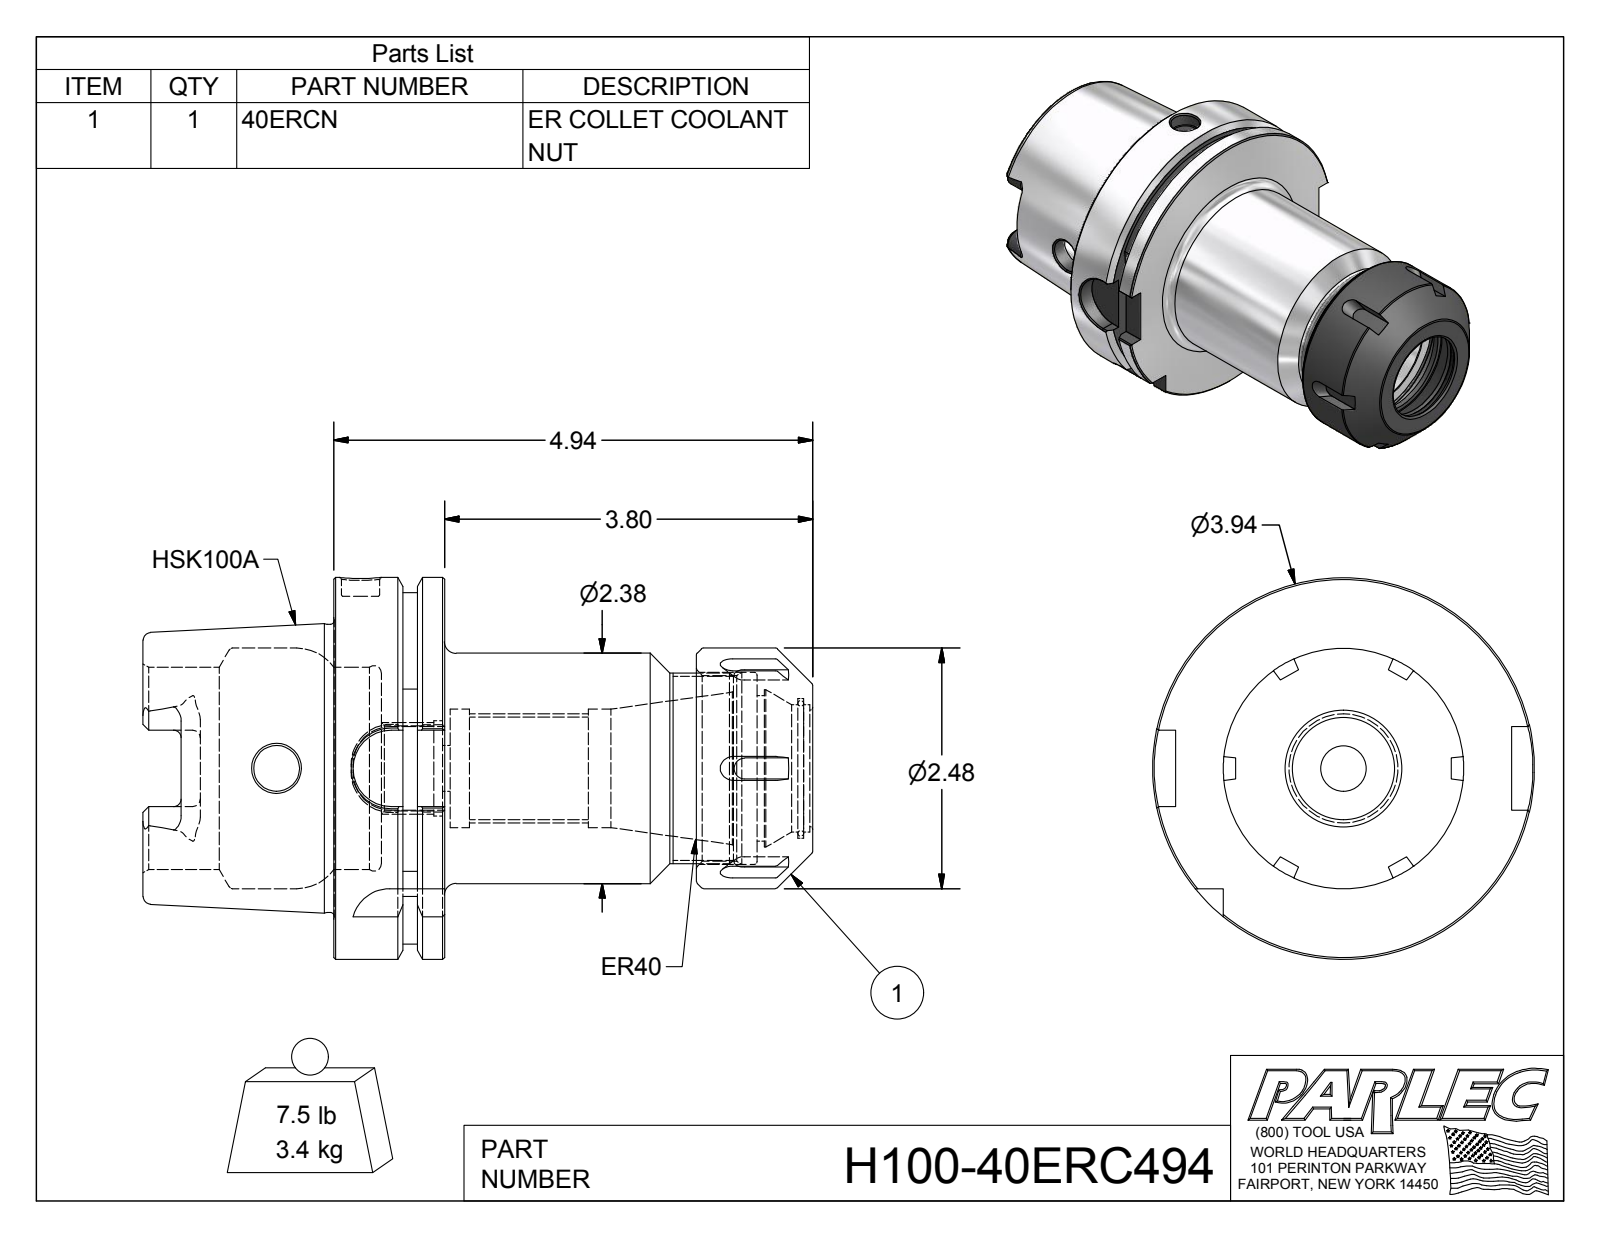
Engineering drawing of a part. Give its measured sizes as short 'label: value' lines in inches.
name: H100-40ERC494; H100-40ER5-1; 40ERCN
written by: Autodesk Inventor 2012 (AUTOMOTIVE_DESIGN)
unit: in
bodies: 2 solids, 188 faces (71 planar, 44 cylindrical, 73 other)
size: 6.909 × 3.937 × 3.937
volume: 26.54 in³; area: 131.2 in²
holes: 2× ⌀0.472, 1× ⌀0.394, 1× ⌀0.881, 1× ⌀0.985, 1× ⌀1.057, 1× ⌀1.22, 1× ⌀1.225, 1× ⌀1.313, 1× ⌀1.437, 1× ⌀1.5, 1× ⌀1.62, 1× ⌀1.916
bosses: 1× ⌀3.937, 1× ⌀2.967, 1× ⌀2.48, 1× ⌀2.375, 1× ⌀1.969
rounds: 6× R0.079, 4× R0.192, 4× R0.394, 1× R1.811
face distances: 1.142, 0.492, 0.65, 1.969, 2.461, 3.11, 6.333, 4.365, 3.873, 3.223
